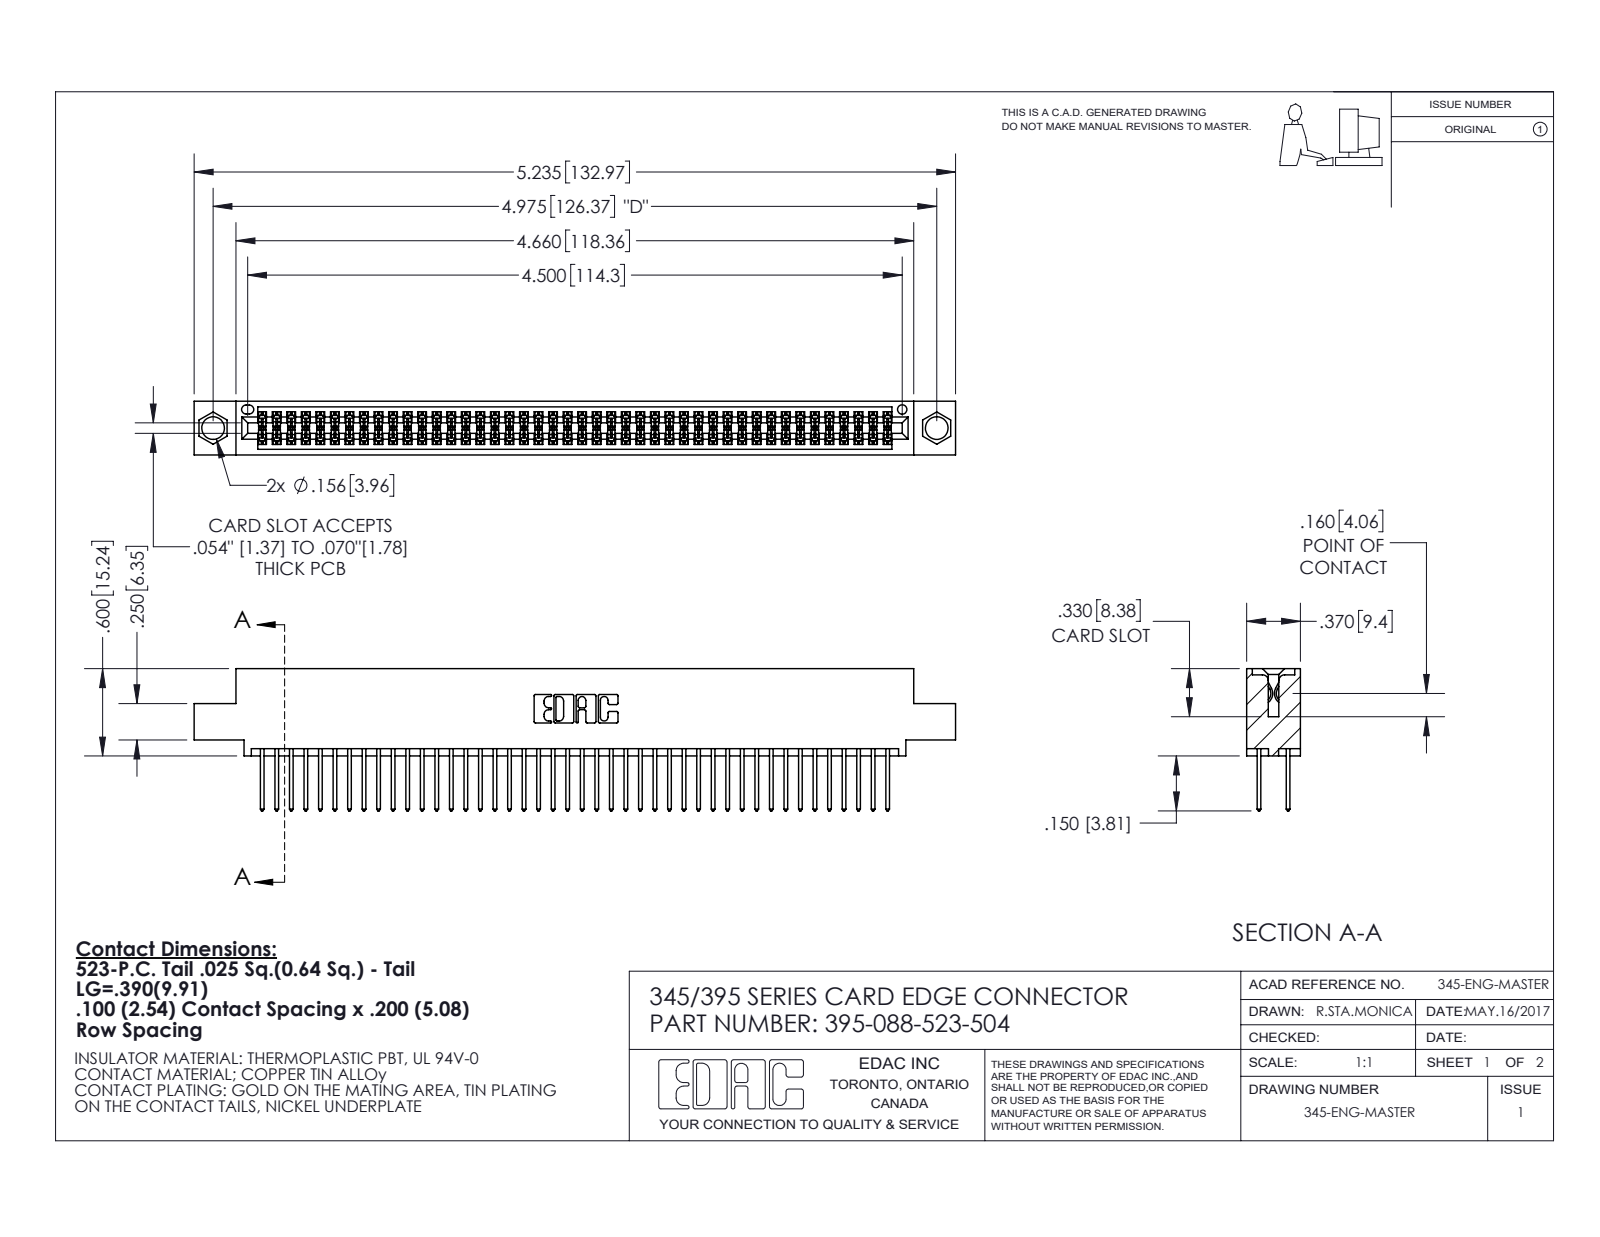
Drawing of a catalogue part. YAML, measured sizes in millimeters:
part_name: "395-088-523-504; 345 Part_0.110 Offset - 0.156 Dia-TI; 345-292-001_345-293-123"
step_written_by: "SolidWorks 2020 (CONFIG_CONTROL_DESIGN)"
units: millimeters
bodies: {solids: 89, faces: 4544, planar: 3002, cylindrical: 1542, other: 0}
overall_size: [133, 24.8, 9.4]
volume: 12900
surface_area: 19920
round_holes:
  - {diameter: 4, count: 2}
  - {diameter: 1.6, count: 1}
partial_cylinders:
  - {radius: 0.2, count: 176}
  - {radius: 0.3, count: 88}
  - {radius: 0.3, count: 22}
  - {radius: 0.2, count: 6}
  - {radius: 0.8, count: 6}
  - {radius: 0.7, count: 3}
  - {radius: 0.4, count: 2}
  - {radius: 0.5, count: 2}
face_to_face_distances: [1.8, 7.6, 5.1, 2.5, 6.9, 0.6, 9.4, 5.7, 4.4, 3.8]
hole_center_spacings: [6.9, 120.4, 126.4]
